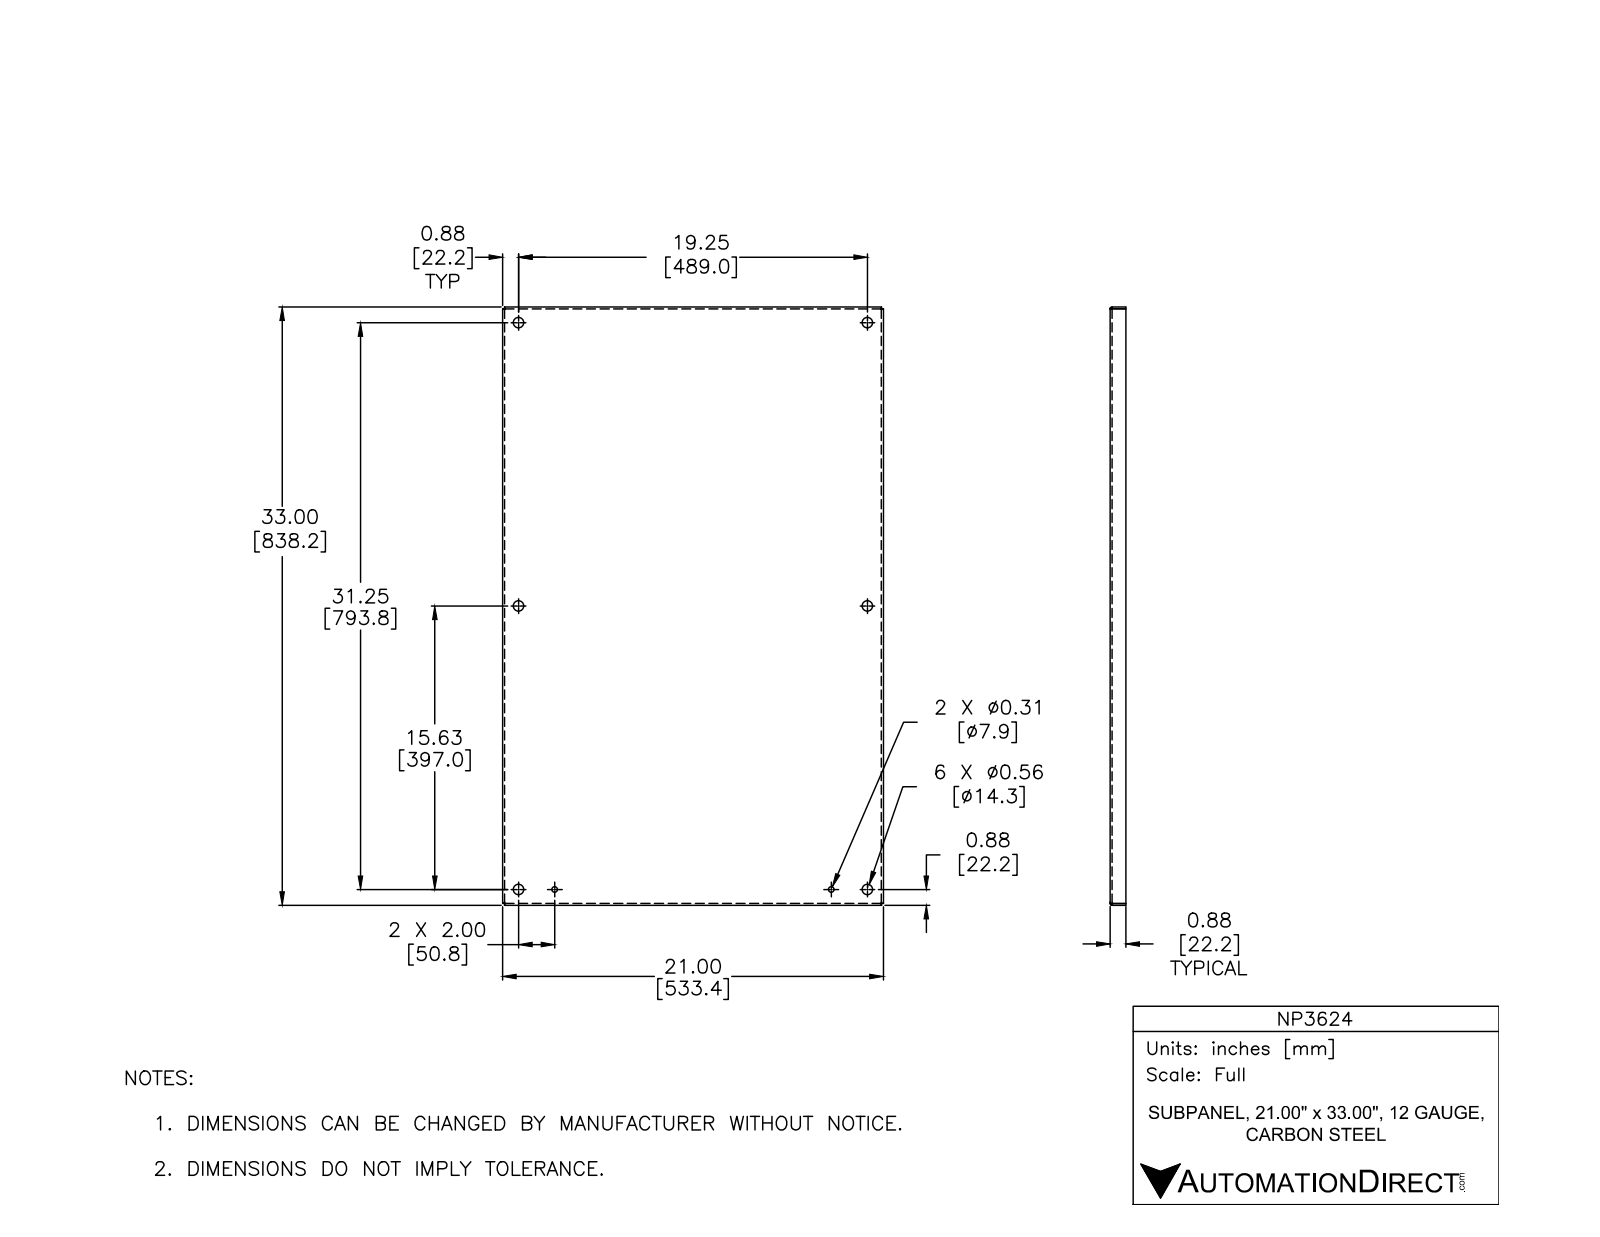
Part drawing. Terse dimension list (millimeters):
name: NP3624
written by: Autodesk Inventor 2012 (AUTOMOTIVE_DESIGN)
unit: mm
bodies: 1 solid, 46 faces (22 planar, 16 cylindrical, 8 other)
size: 838.2 × 533.4 × 22.2
volume: 1 185 000 mm³; area: 1 003 000 mm²
holes: 6× ⌀14.3, 2× ⌀7.9
rounds: 4× R0.8, 4× R3.2
face distances: 2.4, 531, 835.8, 533.4, 528.7, 838.2, 833.5, 19.8, 22.2, 2.7
hole spacings: 396.9, 629.8, 489, 400.1, 591.2, 793.8, 795.4, 906.7
